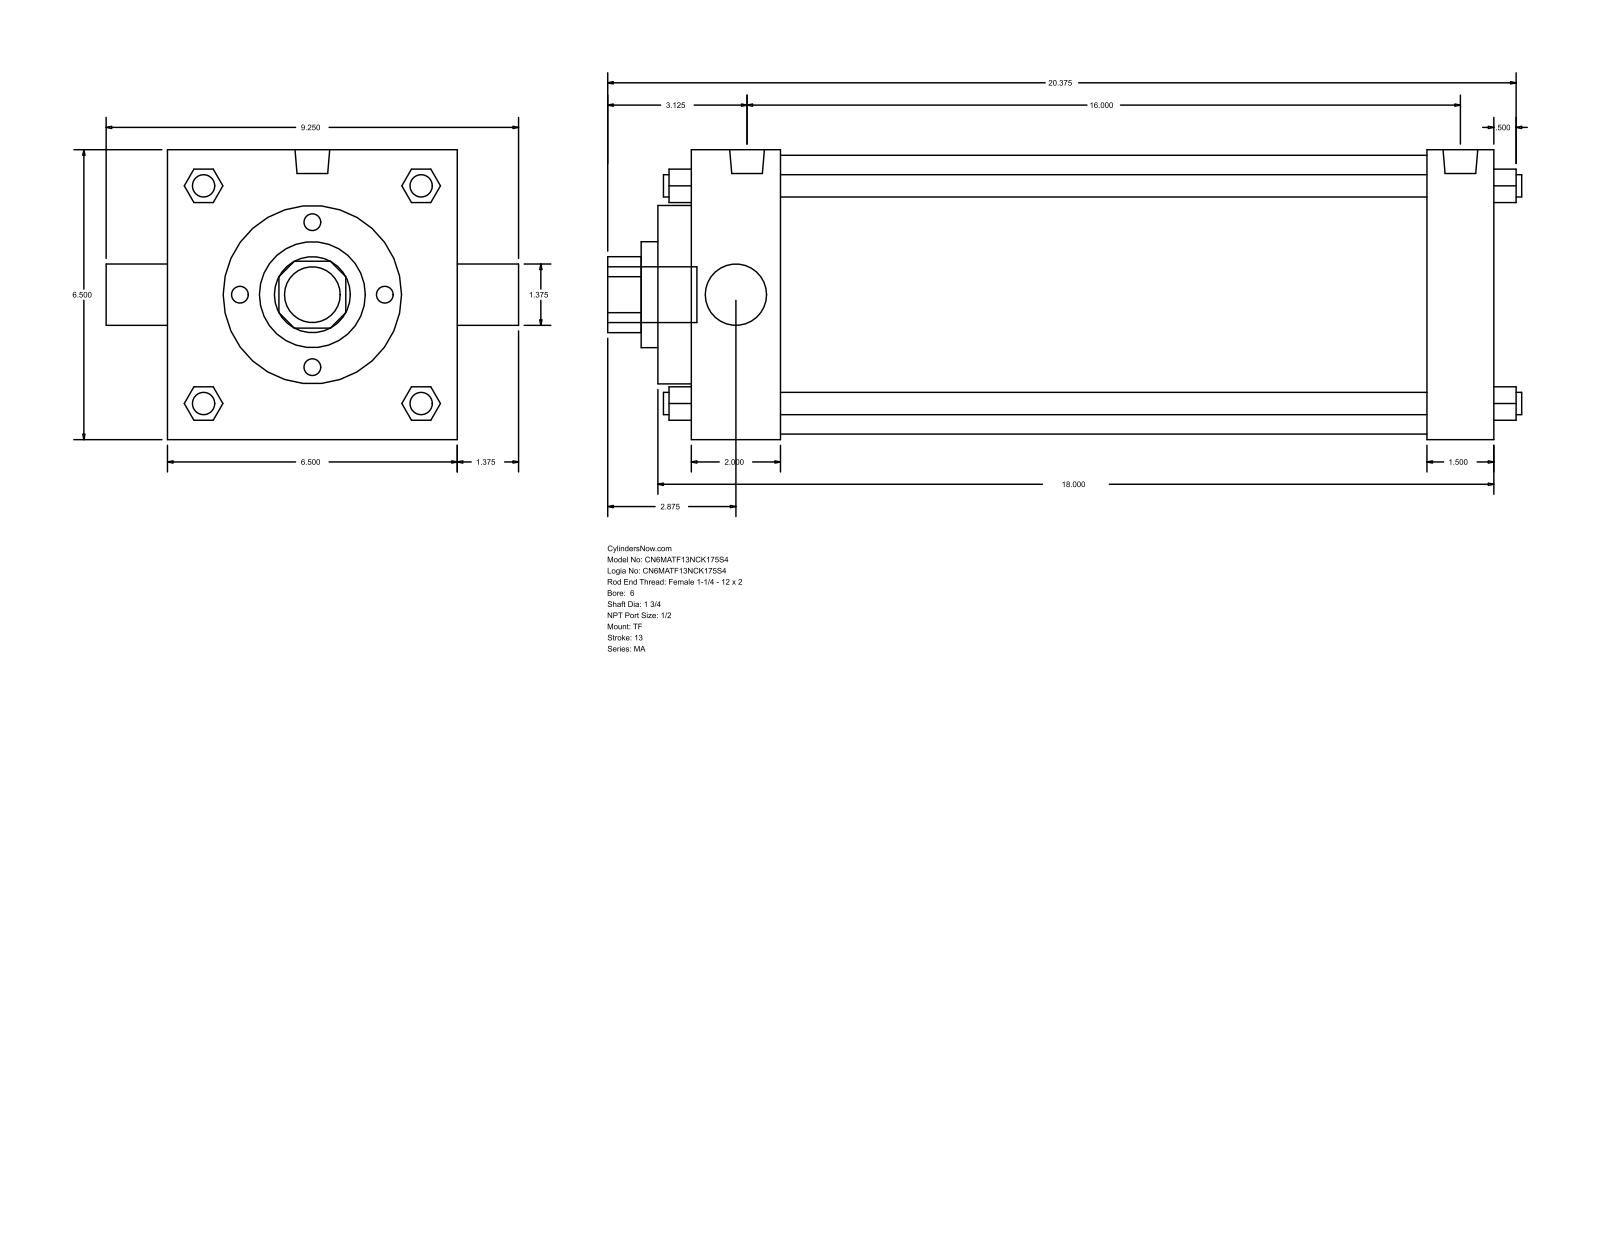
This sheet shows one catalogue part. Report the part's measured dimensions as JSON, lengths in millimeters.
{"part_name": "MA_TF__0600_1.75", "step_written_by": "GSSL Pune (CONFIG_CONTROL_DESIGN)", "units": "millimeters", "bodies": {"solids": 0, "faces": 122, "planar": 93, "cylindrical": 29, "other": 0}, "overall_size": [520.7, 234.95, 165.1], "round_holes": [[34.92, 1], [44.45, 1], [60.33, 1], [101.6, 1], [158.75, 1]], "round_bosses_or_shafts": [[12.7, 4], [17.46, 3], [19.77, 2], [31.75, 1]], "partial_cylinders_radius": [[21.63, 1]], "face_to_face_distances": [165.1, 457.2, 19.05, 50.8, 406.4, 419.11, 368.31, 38.09, 69.85, 438.16]}
